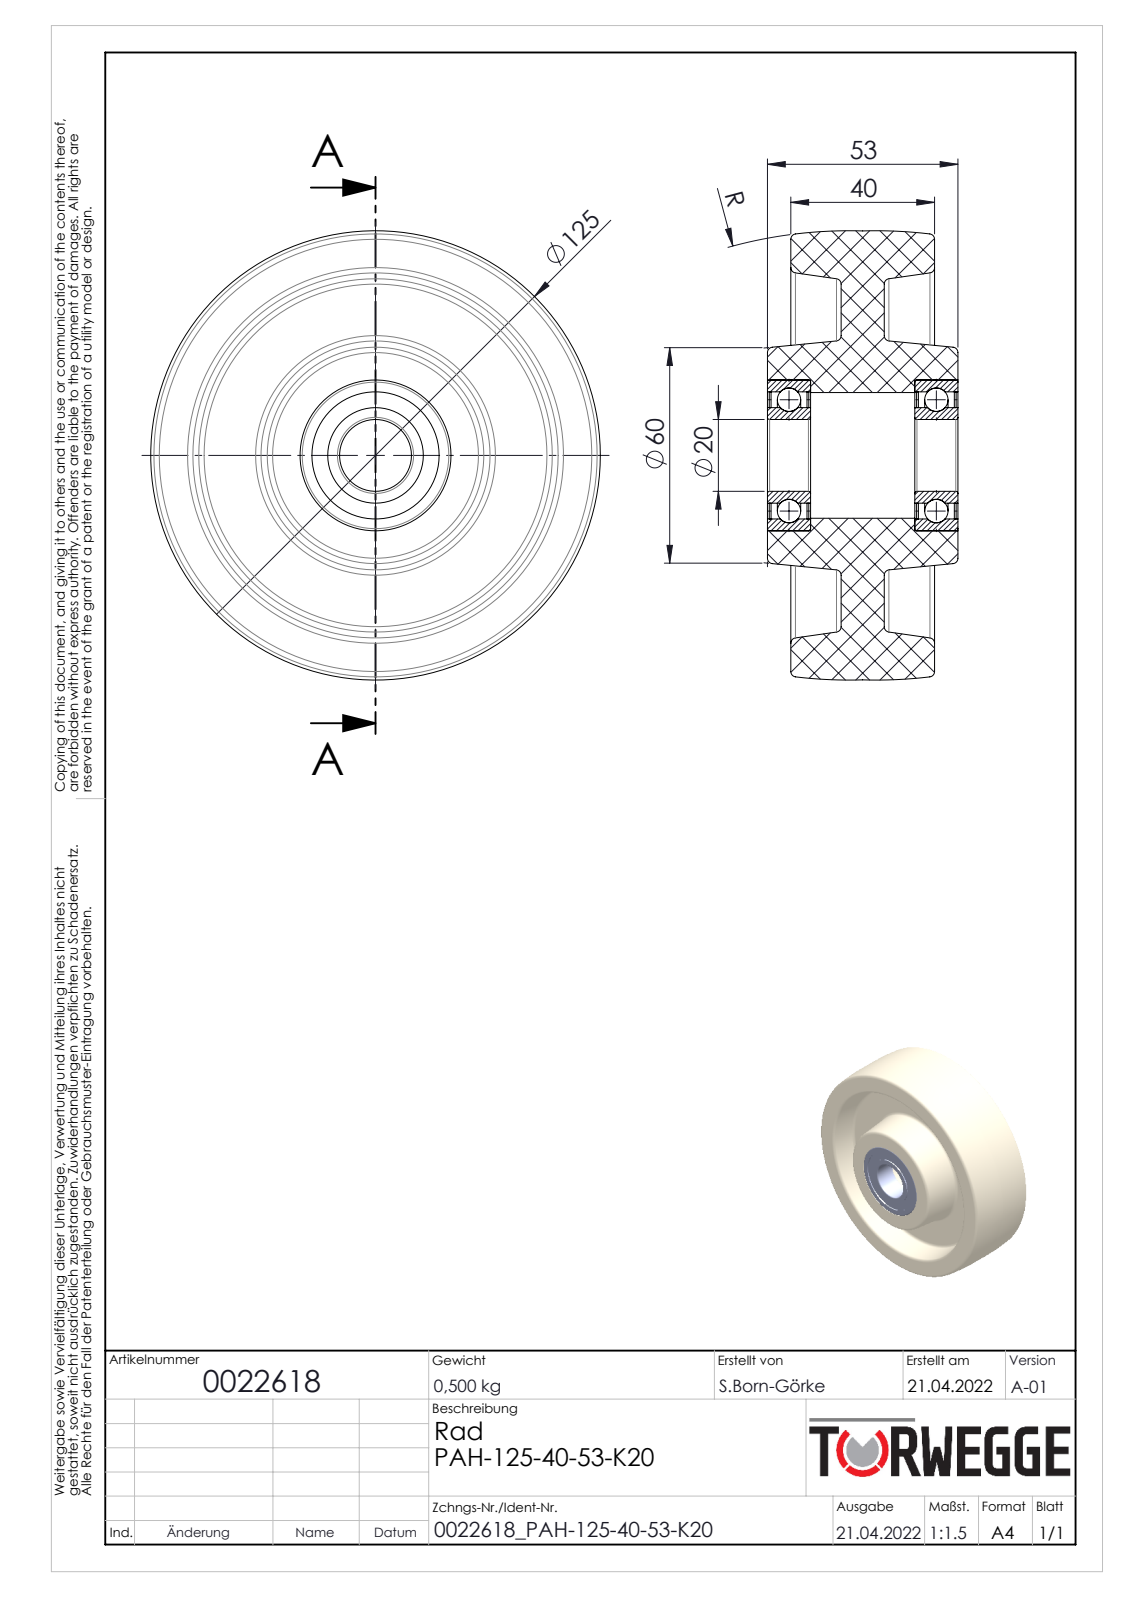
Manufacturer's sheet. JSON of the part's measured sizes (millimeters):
{"part_name": "0022618", "step_written_by": "SolidWorks 2020 (AUTOMOTIVE_DESIGN)", "units": "millimeters", "bodies": {"solids": 11, "faces": 138, "planar": 24, "cylindrical": 46, "other": 68}, "overall_size": [125.11, 125.11, 53], "volume_mm3": 350935, "surface_area_mm2": 77171, "round_holes": [[20, 1], [26.6, 1], [35, 1], [35.4, 1], [42, 1]], "face_to_face_distances": [14, 26, 12, 20.5, 40, 41, 6.5, 32.5, 46.5, 0.5]}
